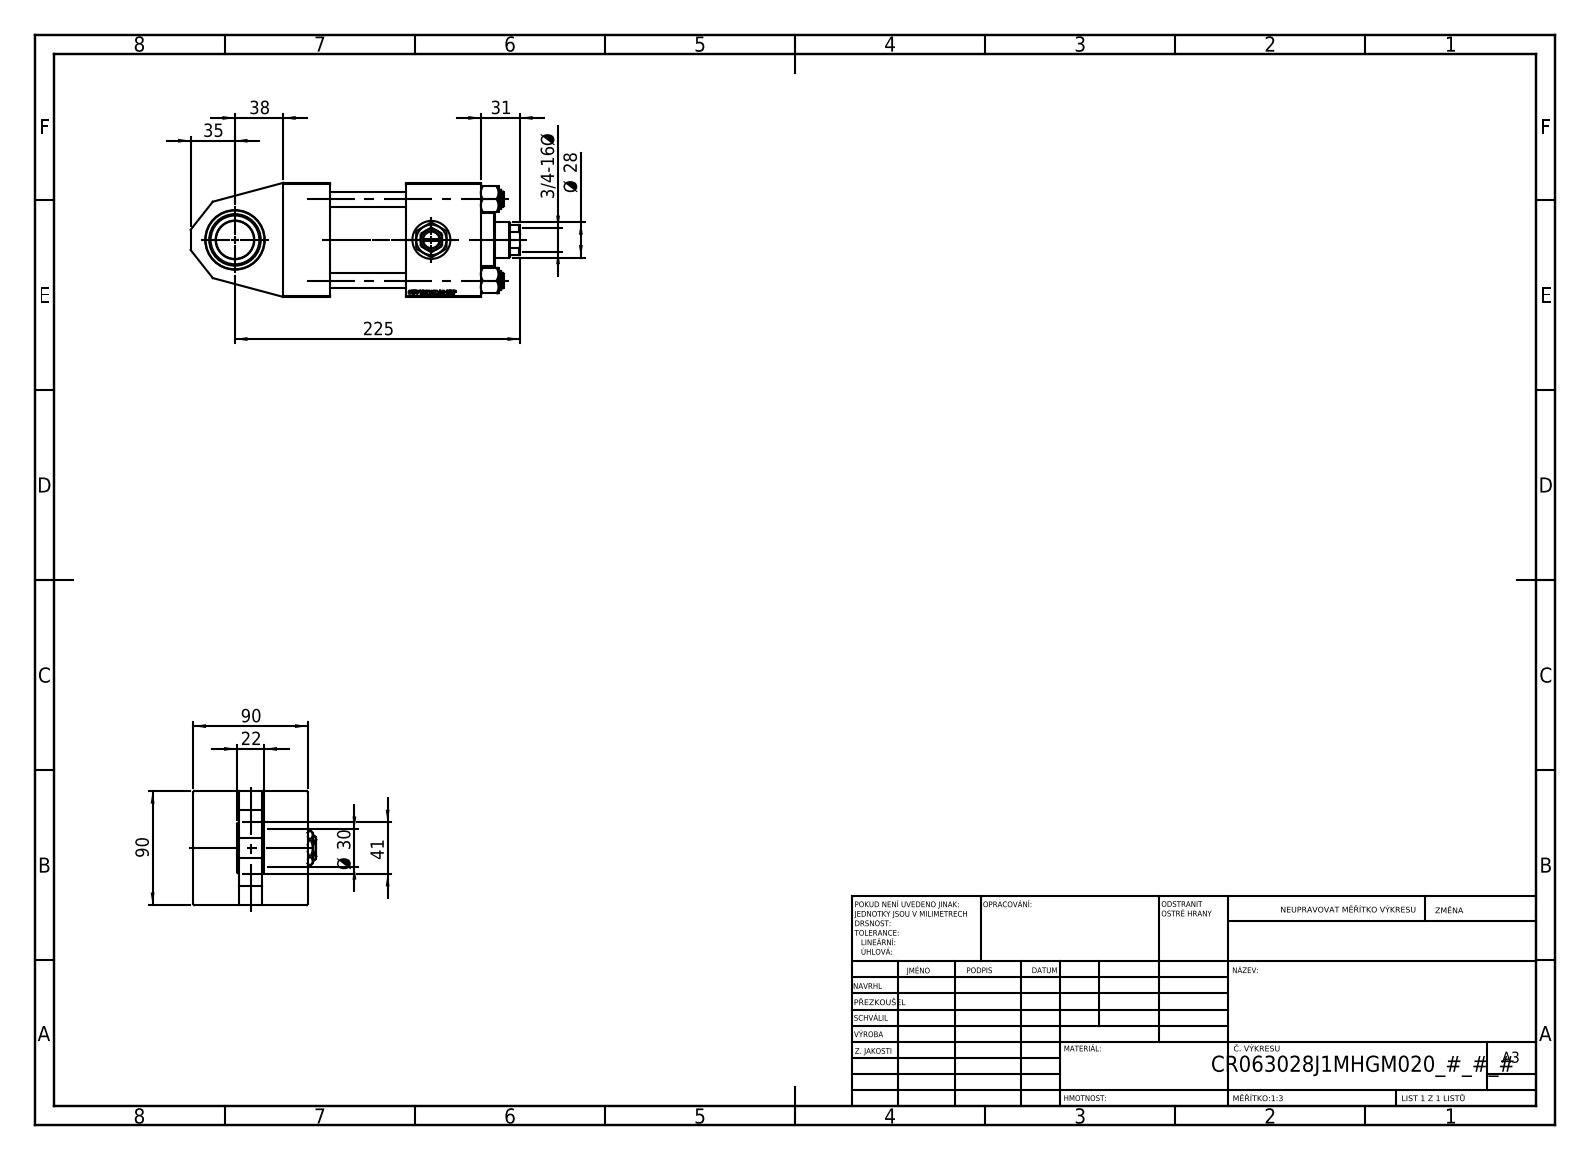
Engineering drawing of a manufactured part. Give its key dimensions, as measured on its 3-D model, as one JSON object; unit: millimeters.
{"part_name": "V215CR_J_VNITRNI_KROUZEK; V215CR_VCP_J; V215CR_TYCINKA_J; NUT_M5_J (+3 more)", "step_written_by": "SolidWorks 2019 (CONFIG_CONTROL_DESIGN)", "units": "millimeters", "bodies": {"solids": 13, "faces": 1193, "planar": 540, "cylindrical": 93, "other": 560}, "overall_size": [260, 97, 90], "volume_mm3": 1029000, "surface_area_mm2": 202665, "round_holes": [[12, 4], [30, 3], [2.5, 2], [7, 2], [20.96, 2], [18.5, 1], [28, 1], [31, 1], [47, 1], [50, 1], [60, 1], [63, 1]], "round_bosses_or_shafts": [[15, 4], [69, 1], [42, 1]], "partial_cylinders_radius": [[13.5, 1]], "face_to_face_distances": [90, 54, 36, 119, 37, 156, 97, 60, 59, 18], "hole_center_spacings": [32.39, 45.47, 64.3, 68.42, 28.25, 56.5, 90.93, 98.5]}
